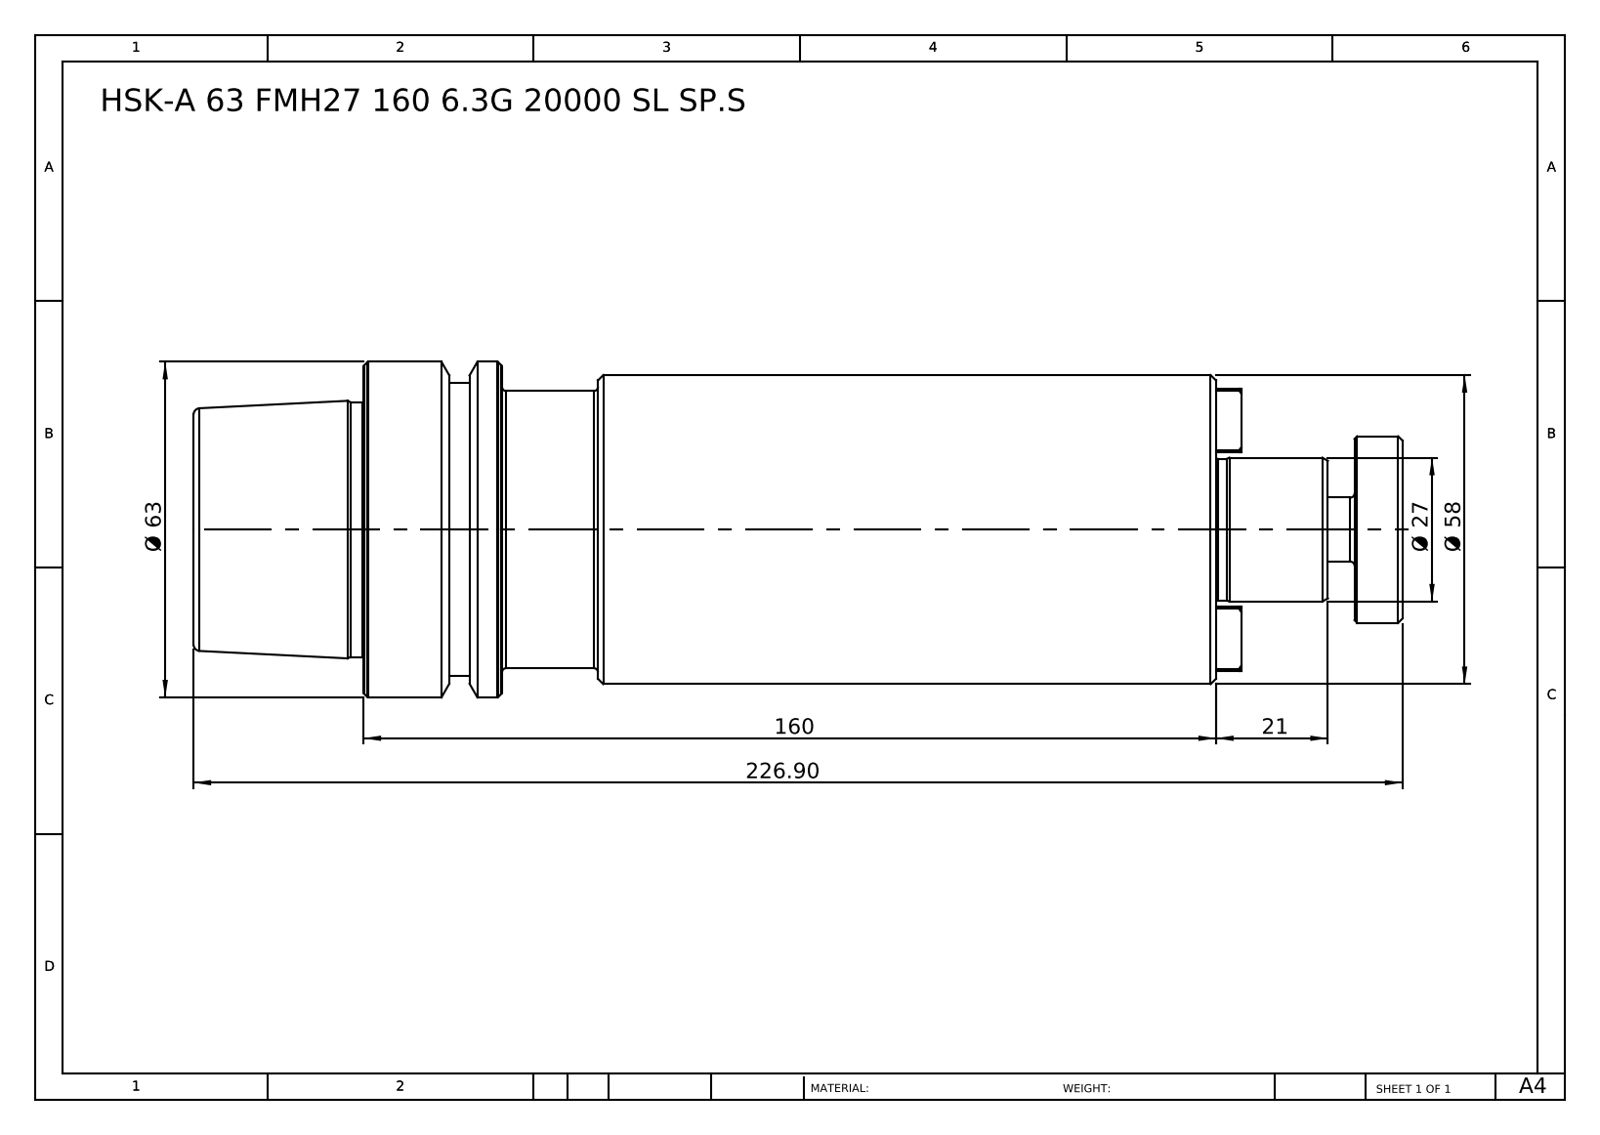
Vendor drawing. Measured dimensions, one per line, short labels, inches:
name: HSK-A 63 FMH27 160 6.3G 20000 SL SP.S
written by: SolidWorks 2014 (CONFIG_CONTROL_DESIGN)
unit: in
bodies: 1 solid, 106 faces (38 planar, 20 cylindrical, 48 other)
size: 8.933 × 2.48 × 2.48
volume: 30.49 in³; area: 71.96 in²
bosses: 1× ⌀2.48, 1× ⌀2.283, 1× ⌀2.165, 1× ⌀2.047, 1× ⌀1.881, 1× ⌀1.378, 1× ⌀1.063, 1× ⌀1.047
face distances: 7.555, 1.024, 6.299, 1.378, 8.933, 0.354, 8.579, 7.677, 7.323, 1.256
